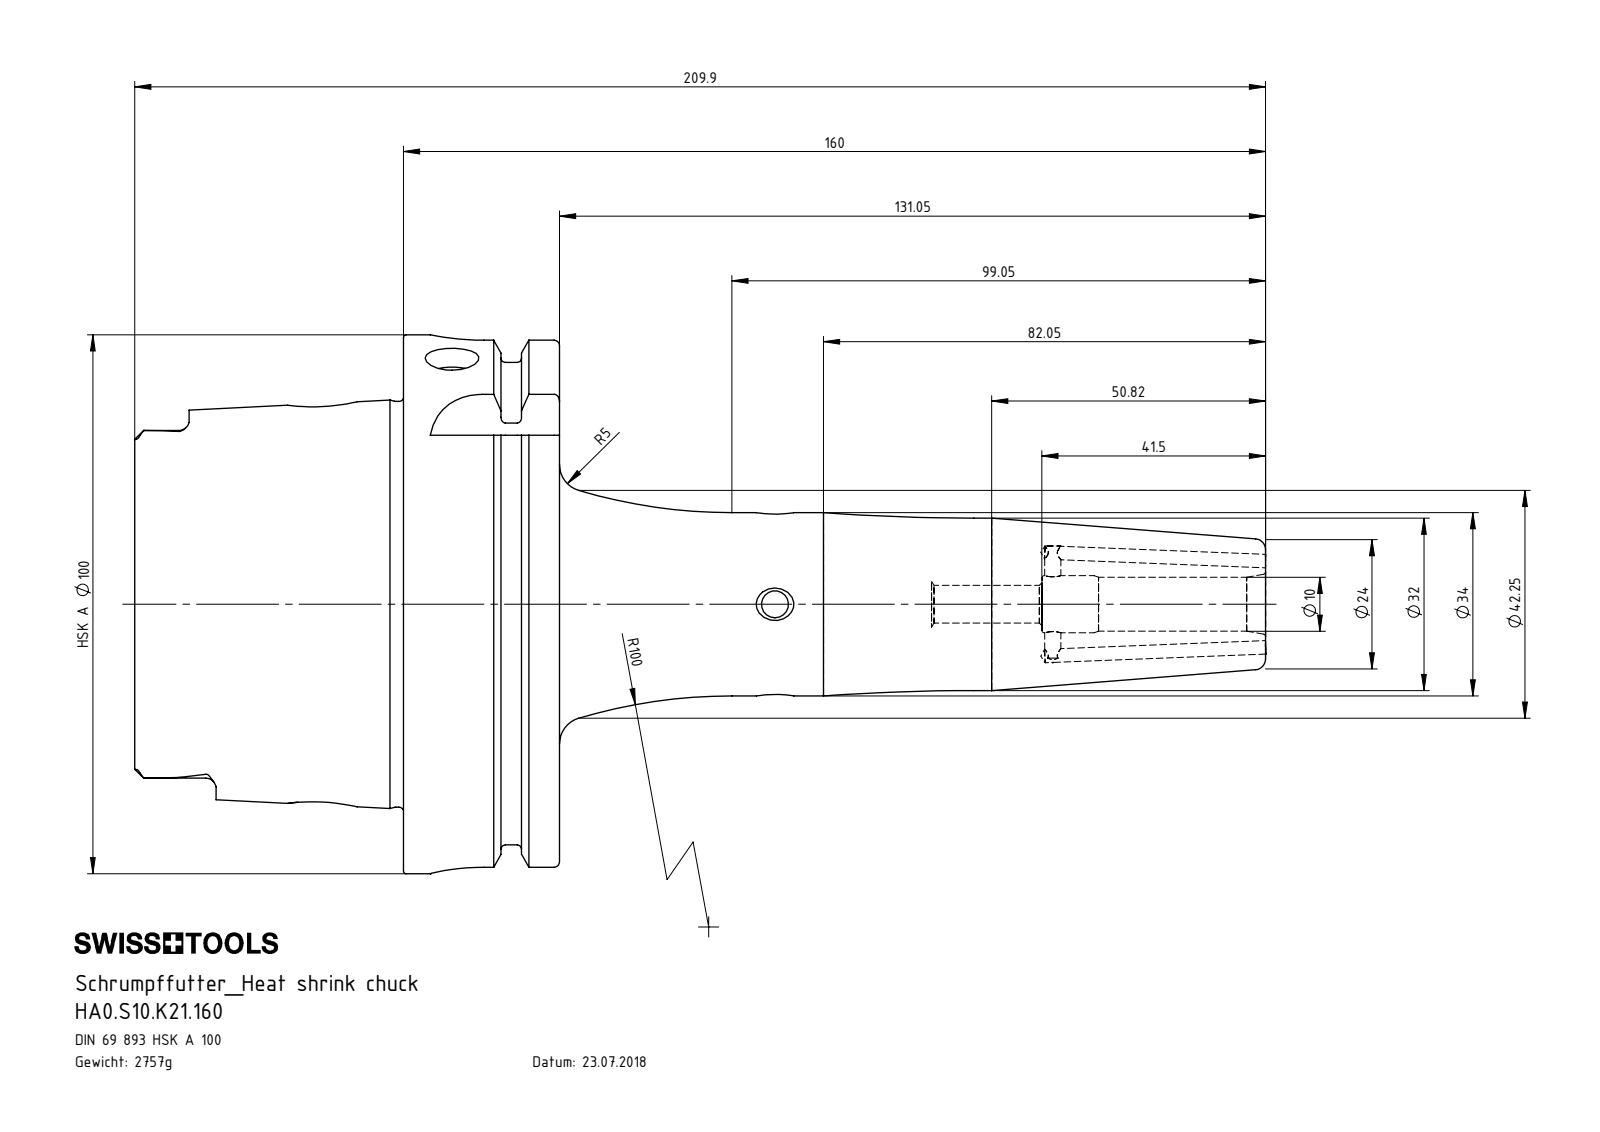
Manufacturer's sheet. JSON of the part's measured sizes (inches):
{"part_name": "HA0.S10.K21.160; ERU-CJ2.001.006; ERU-AN3.K01.020_A; HA0-S10.K21.160_C_Fertigbearbeitung", "step_written_by": "SolidWorks 2017 (CONFIG_CONTROL_DESIGN)", "units": "inches", "bodies": {"solids": 4, "faces": 305, "planar": 95, "cylindrical": 88, "other": 122}, "overall_size": [8.267, 3.937, 3.937], "volume_in3": 21.43, "surface_area_in2": 105.4, "round_holes": [[0.394, 4], [0.098, 2], [0.197, 2], [0.472, 2], [0.118, 1], [0.157, 1], [0.276, 1], [0.335, 1], [0.417, 1], [0.886, 1], [1.024, 1], [2.087, 1]], "round_bosses_or_shafts": [[0.118, 2], [3.937, 1], [3.62, 1], [2.963, 1], [1.339, 1], [1.26, 1], [0.315, 1]], "partial_cylinders_radius": [[0.075, 6], [0.192, 4], [0.394, 4]], "face_to_face_distances": [1.14, 0.65, 0.49, 1.965, 2.455, 3.104, 3.457, 3.079, 1.114, 0.624], "hole_center_spacings": [2.03, 2.439, 3.305, 5.335]}
